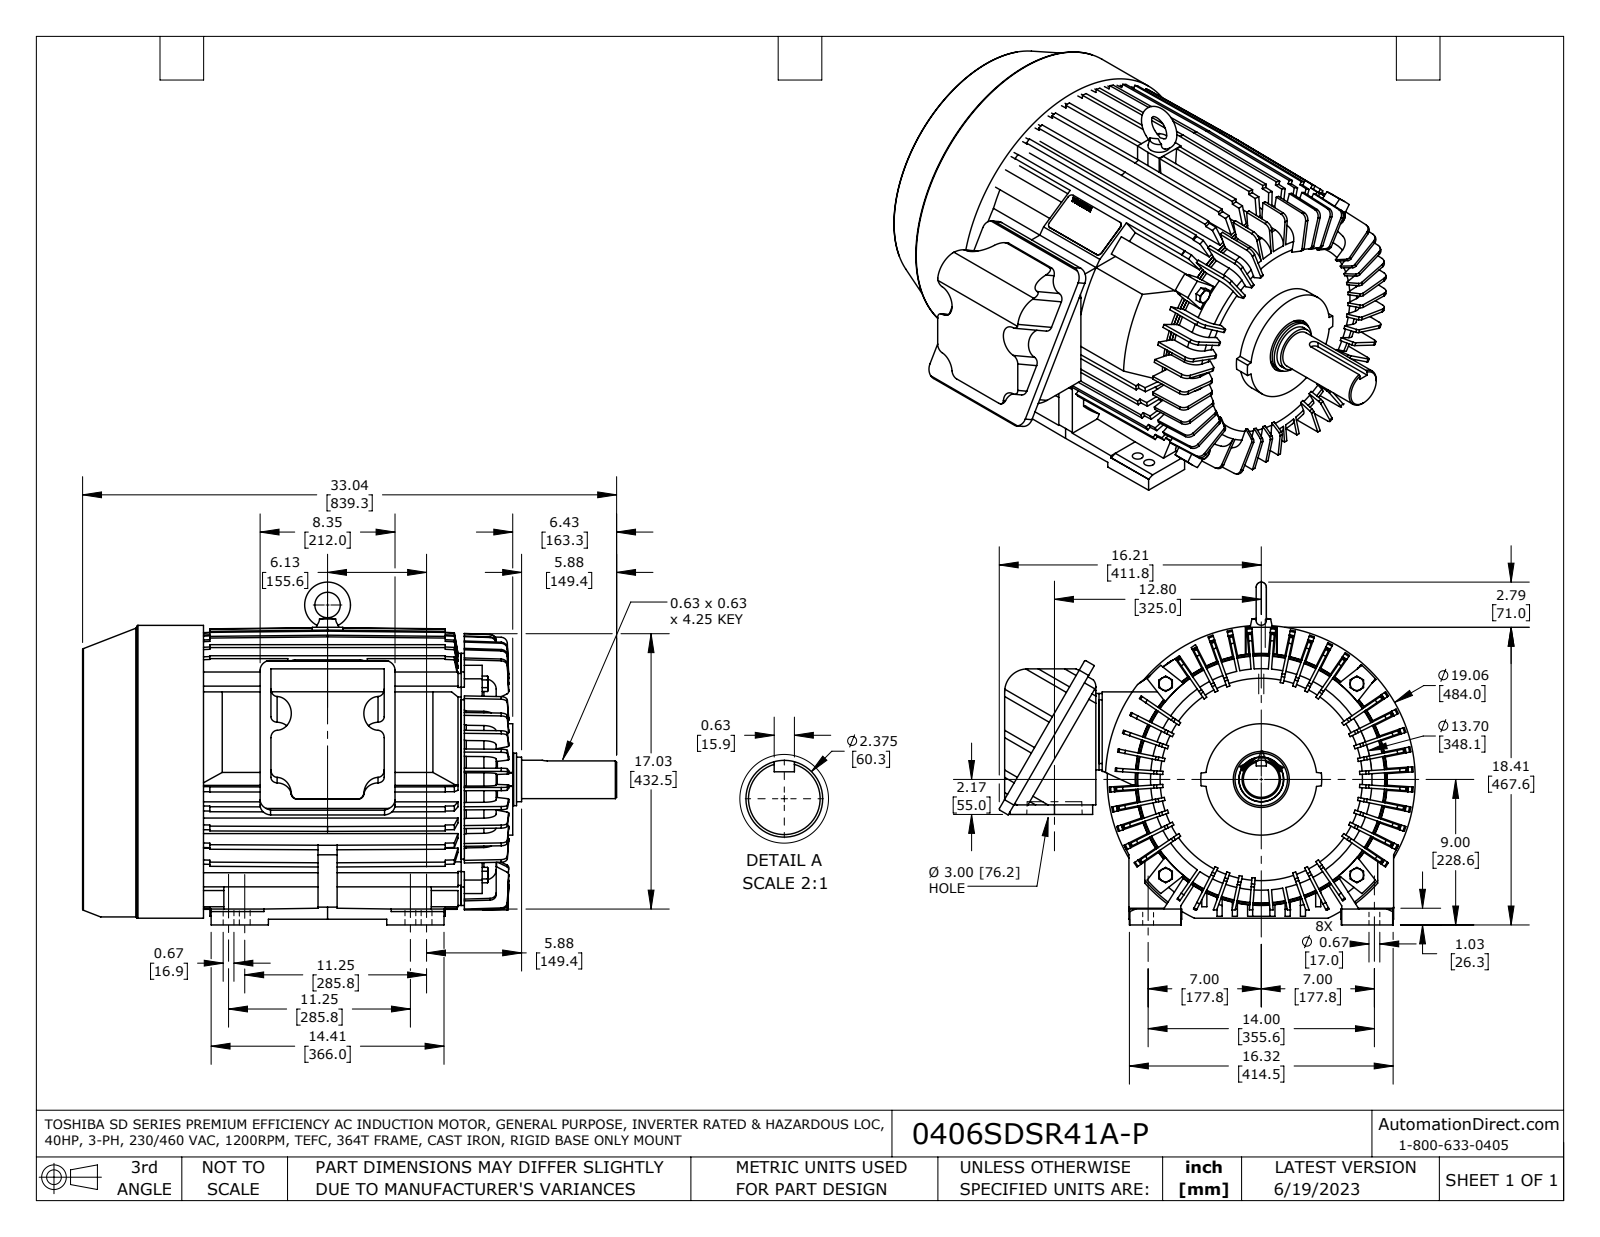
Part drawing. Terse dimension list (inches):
name: MDSLV001-07-46P-F1-Bottom nc bod broke rep1a
written by: SolidWorks 2021 (AUTOMOTIVE_DESIGN)
unit: in
bodies: 13 solids, 3444 faces (2612 planar, 255 cylindrical, 577 other)
size: 33.042 × 25.739 × 21.205
volume: 6 793 in³; area: 5 998 in²
holes: 8× ⌀0.354, 8× ⌀0.669, 4× ⌀0.087, 4× ⌀0.398, 4× ⌀0.551, 1× ⌀0.472, 1× ⌀0.681, 1× ⌀1.26, 1× ⌀2.756, 1× ⌀2.776, 1× ⌀3.465, 1× ⌀3.937
bosses: 1× ⌀19.055, 1× ⌀15.591, 1× ⌀15.157, 1× ⌀6.89, 1× ⌀3.346, 1× ⌀3.248, 1× ⌀3.228, 1× ⌀2.795
rounds: 26× R0.394, 6× R0.021, 6× R0.042, 6× R0.055, 6× R0.906, 4× R0.02, 4× R0.09, 4× R0.25
face distances: 0.315, 0.591, 15.945, 16.535, 16.26, 15.669, 0.276, 6.89, 0.059, 0.197
hole spacings: 11.222, 0.886, 1, 2.363, 3.341, 7.48, 8.366, 8.676
